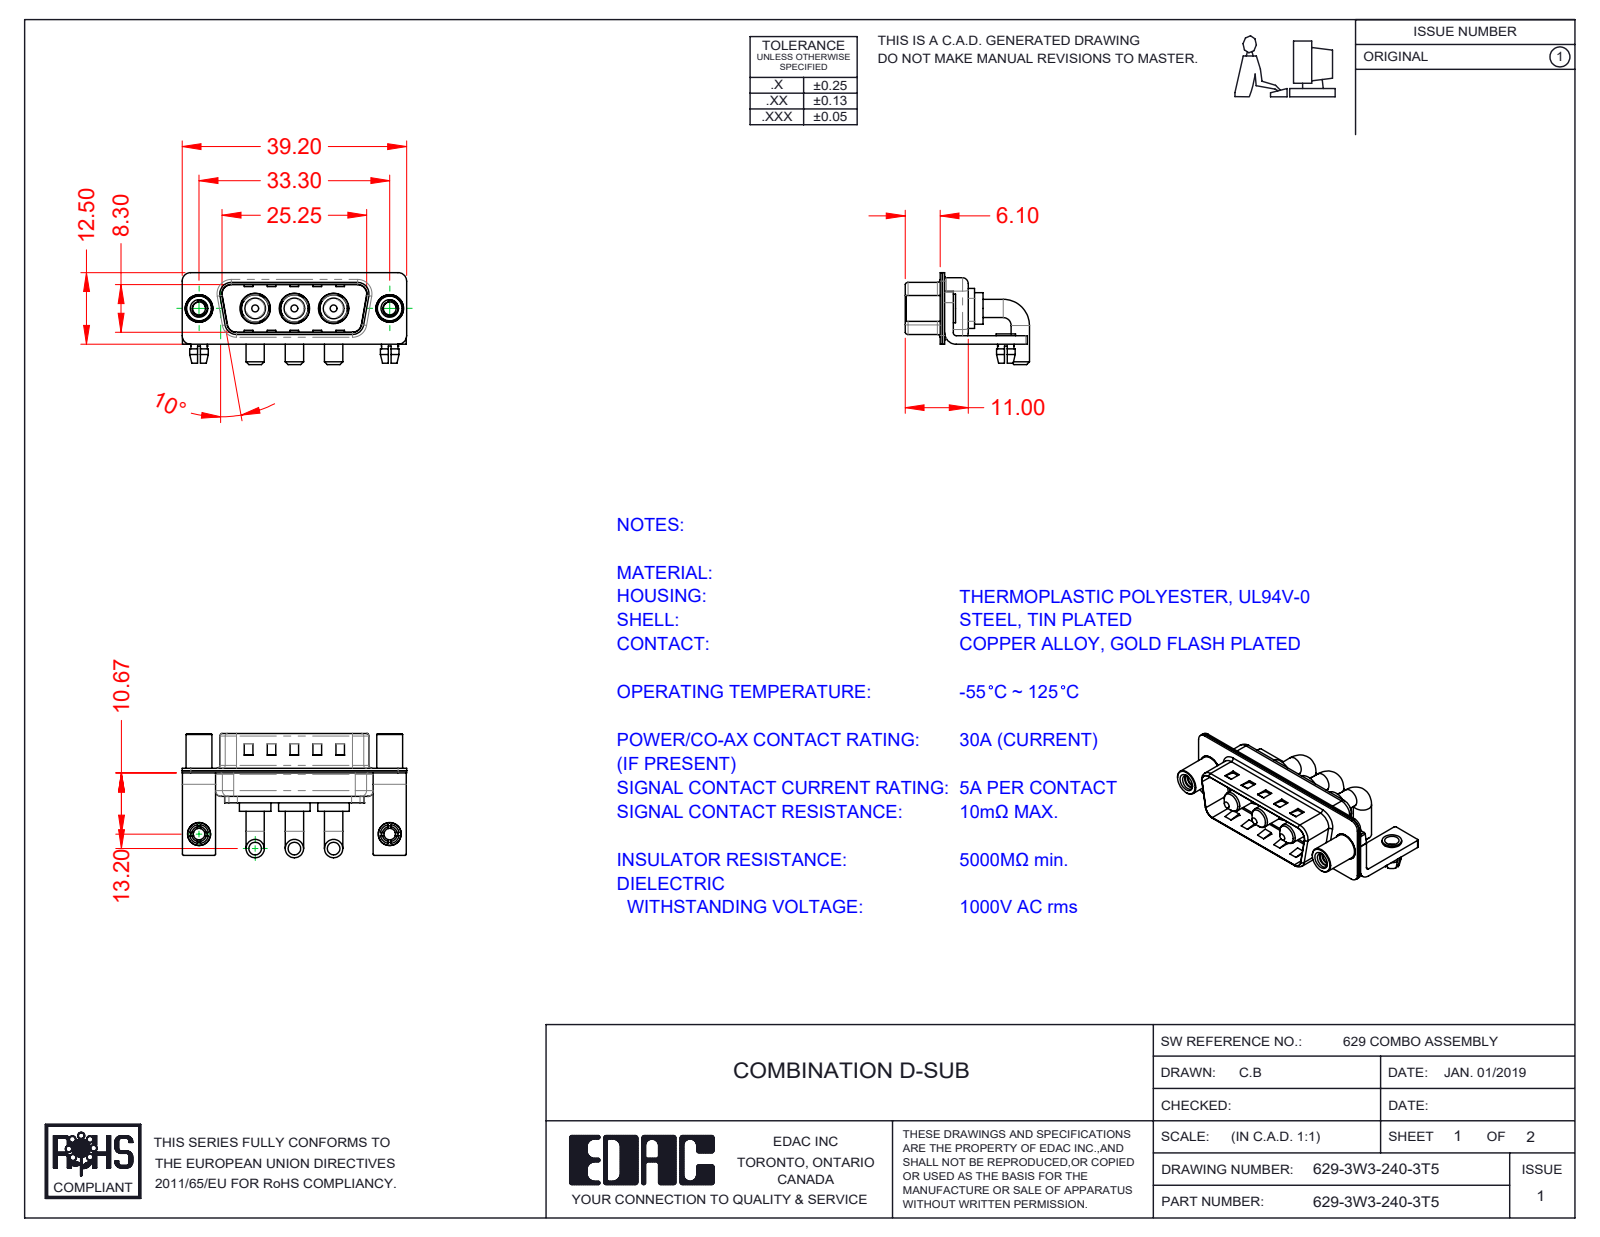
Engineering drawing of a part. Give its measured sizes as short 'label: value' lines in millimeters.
name: 629Combo Housing_3W3; 629Combo Shell Front_15 Contacts; 629Combo Shell Rear_15 Contacts; 629-3W3-240-3T5 (+4 more)
written by: SolidWorks 2020 (CONFIG_CONTROL_DESIGN)
unit: mm
bodies: 15 solids, 649 faces (239 planar, 288 cylindrical, 122 other)
size: 39.2 × 21.7 × 16.05
volume: 2 769 mm³; area: 6 170 mm²
holes: 3× ⌀4.85, 3× ⌀5.3, 2× ⌀2, 2× ⌀2.26, 2× ⌀2.5, 2× ⌀3.2, 2× ⌀4, 2× ⌀4.8
bosses: 6× ⌀3.2, 3× ⌀5.5, 3× ⌀5.2, 3× ⌀4.75, 3× ⌀3.75, 3× ⌀3.6, 2× ⌀5, 2× ⌀4.9
rounds: 16× R0.25, 16× R1.5, 13× R2, 9× R0.5, 8× R1.6, 4× R0.6, 4× R0.65, 4× R0.9
face distances: 0.4, 0.8, 1.5, 9.5, 8.7, 9.1, 9.9, 5.2, 0.75, 0.6
hole spacings: 6.85, 9.8, 16.65, 23.5, 33.3, 13.7
